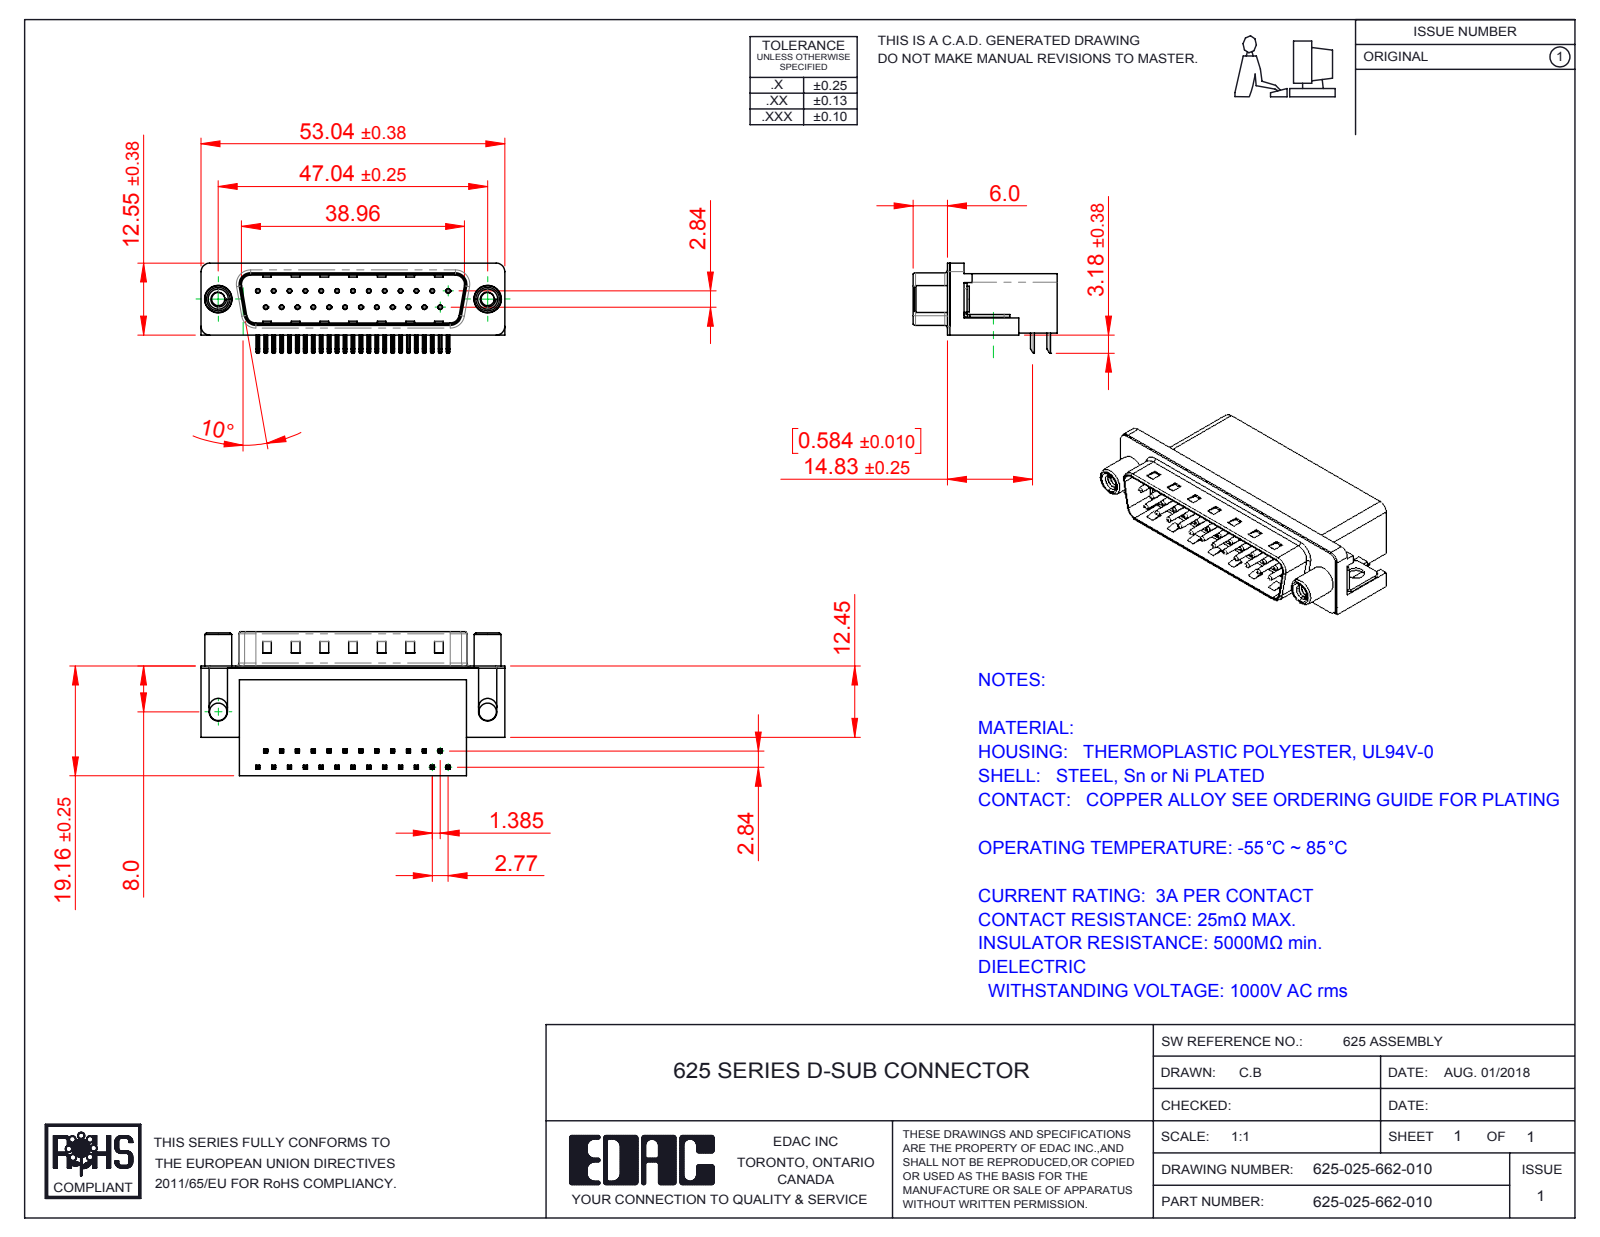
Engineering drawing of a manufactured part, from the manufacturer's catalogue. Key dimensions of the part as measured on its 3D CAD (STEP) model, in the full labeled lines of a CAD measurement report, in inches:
Part name (STEP PRODUCT): 625-025-662-010; 625 Housing_25 Socket; 625 Contact Top; 625 Thru Hole Board Mount (+3 more)
STEP written by: SolidWorks 2016 (CONFIG_CONTROL_DESIGN)
Units: inches
Bodies: 31 solids, 2259 faces (1397 planar, 669 cylindrical, 193 other)
Overall size (bounding box): 2.088 × 0.991 × 0.619
Volume: 0.565 in³ · Surface area: 14.02 in²
Round holes (diameter × count): ⌀0.014 ×25, ⌀0.031 ×25, ⌀0.091 ×2, ⌀0.12 ×2, ⌀0.122 ×2, ⌀0.157 ×2, ⌀0.189 ×2, ⌀0.197 ×2
Round bosses / shafts (diameter × count): ⌀0.03 ×25, ⌀0.193 ×2, ⌀0.185 ×2, ⌀0.177 ×2, ⌀0.152 ×2
Partial cylindrical surfaces — rounded edges, fillets, slot ends (radius × count): R0.01 ×100, R0.005 ×50, R0.039 ×16, R0.02 ×9, R0.063 ×8, R0.059 ×7, R0.035 ×4, R0.079 ×4
Main face-to-face distances: 0.016, 0.407, 0.739, 0.083, 0.345, 0.412, 0.428, 0.067, 0.754, 0.114
Hole centre spacings: 0.124, 0.109, 0.436, 0.218, 0.327, 0.198, 0.545, 0.294
